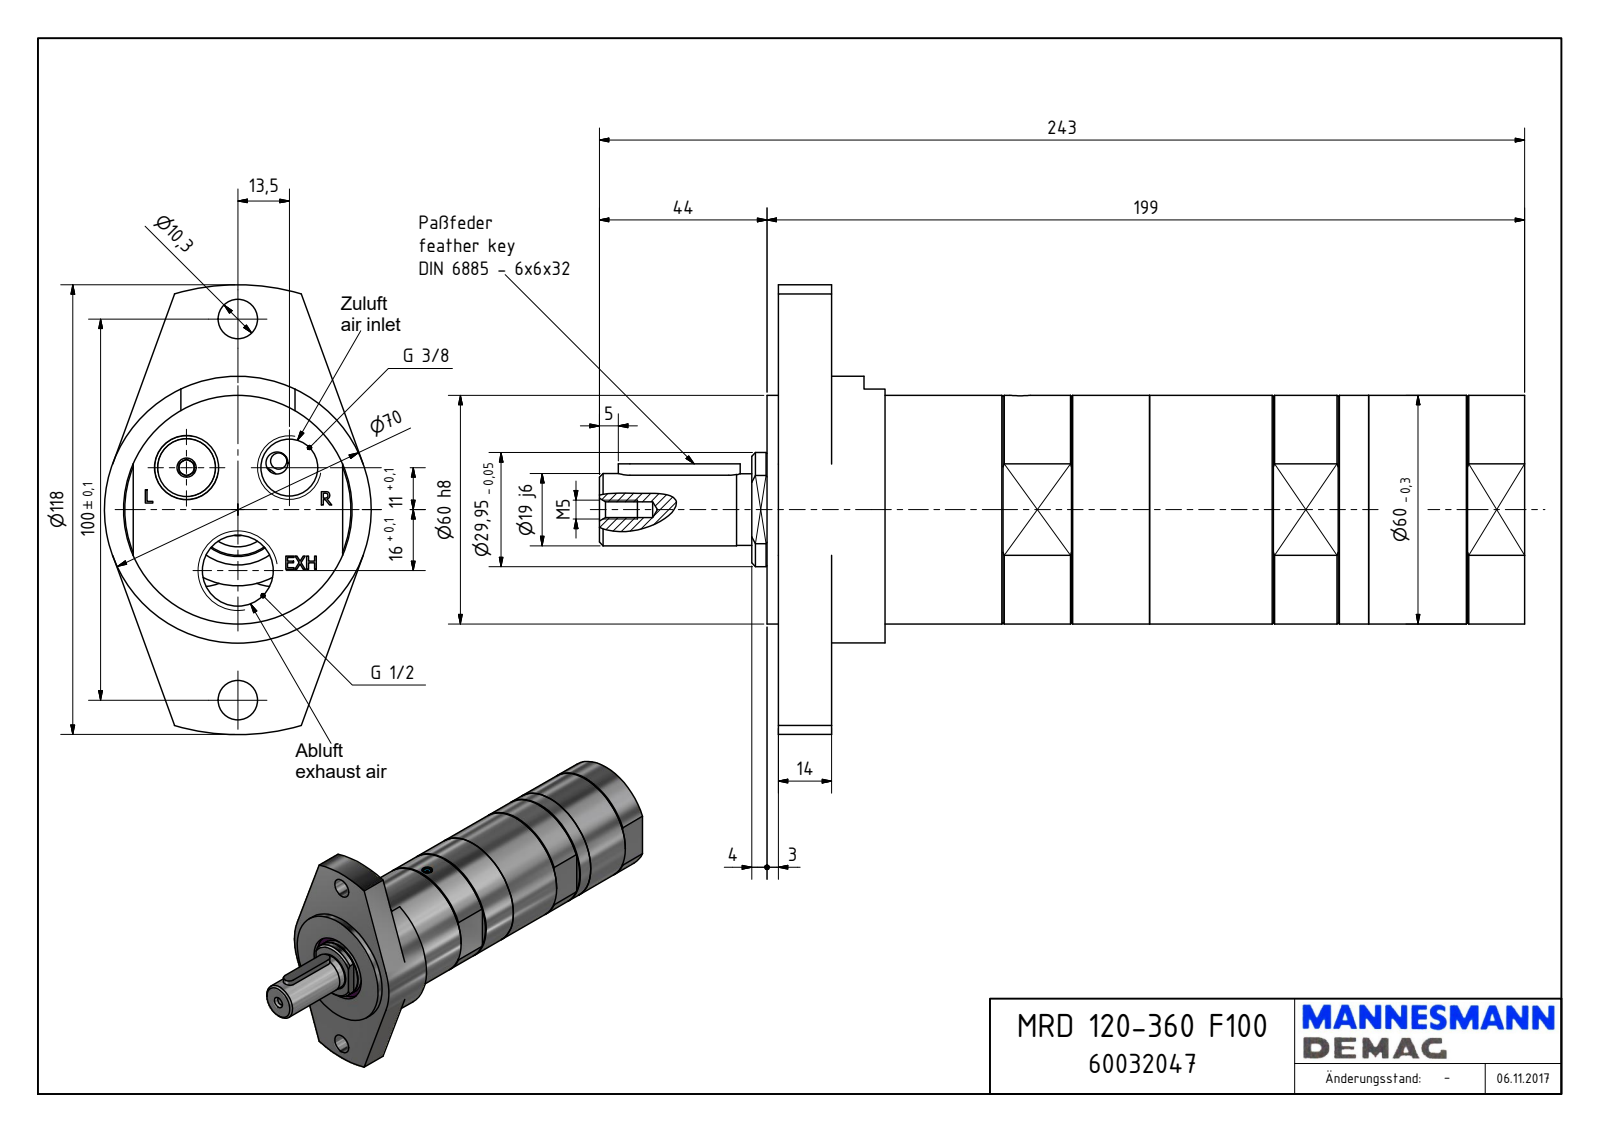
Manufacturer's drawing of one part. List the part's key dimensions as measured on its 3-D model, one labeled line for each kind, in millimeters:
Part name (STEP PRODUCT): MRD 120-360 F100_60032047
STEP written by: Autodesk Inventor 2018 (AUTOMOTIVE_DESIGN)
Units: millimetres
Bodies: 1 solid, 218 faces (128 planar, 48 cylindrical, 42 other)
Overall size (bounding box): 243 × 118 × 70
Volume: 618 293 mm³ · Surface area: 62 219 mm²
Round holes (diameter × count): ⌀4 ×2, ⌀10.3 ×2, ⌀14.95 ×2, ⌀1.55 ×1, ⌀4.13 ×1, ⌀5.5 ×1, ⌀18.63 ×1, ⌀35 ×1
Round bosses / shafts (diameter × count): ⌀70 ×1, ⌀60 ×1, ⌀55.18 ×1, ⌀29.95 ×1, ⌀19 ×1, ⌀18.8 ×1, ⌀5 ×1, ⌀3.6 ×1
Partial cylindrical surfaces — rounded edges, fillets, slot ends (radius × count): R3 ×2, R7.5 ×2, R8.5 ×1, R19.38 ×1, R23.5 ×1, R25.89 ×1, R59 ×1
Main face-to-face distances: 14, 196, 182, 3, 17, 199, 55, 31, 28, 168
Hole centre spacings: 17.41, 30.19, 41.27, 50, 62.48, 16, 27, 34
